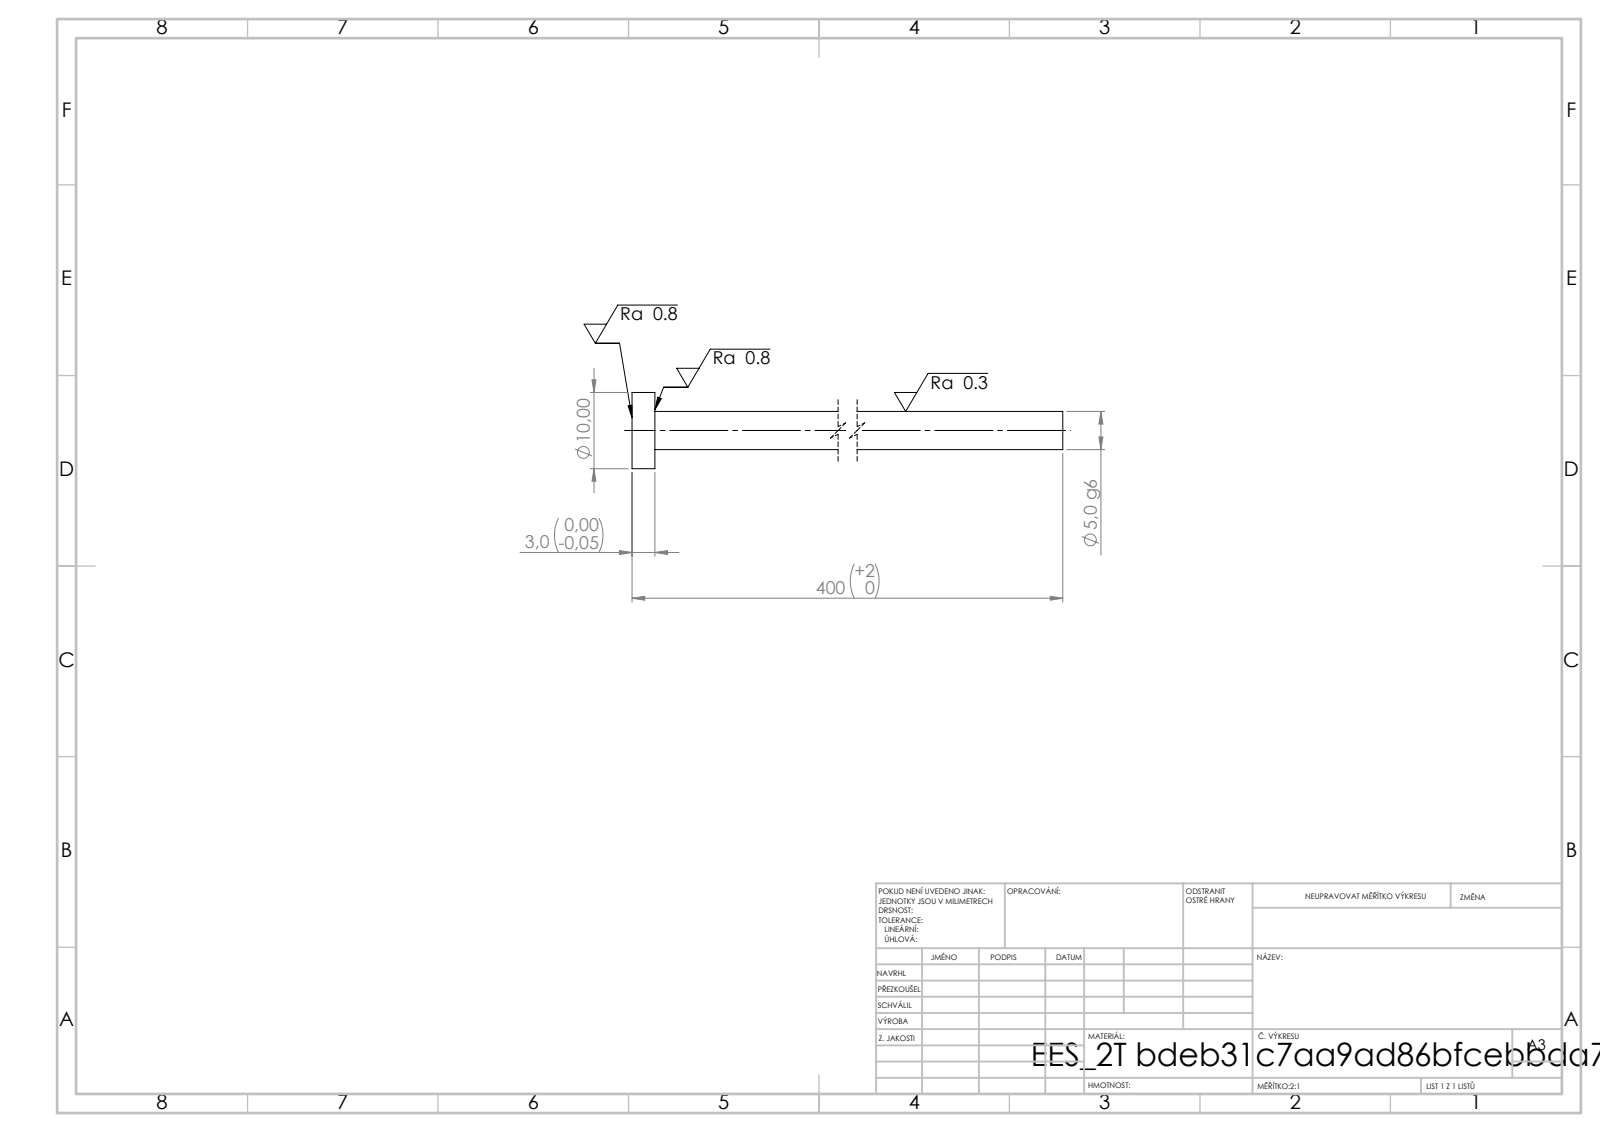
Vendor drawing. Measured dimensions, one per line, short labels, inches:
written by: SolidWorks 2019 (CONFIG_CONTROL_DESIGN)
unit: in
bodies: 1 solid, 7 faces (3 planar, 4 cylindrical, 0 other)
size: 15.748 × 0.394 × 0.394
volume: 0.49 in³; area: 10.05 in²
bosses: 1× ⌀0.394, 1× ⌀0.197
face distances: 0.118, 15.748, 15.63
